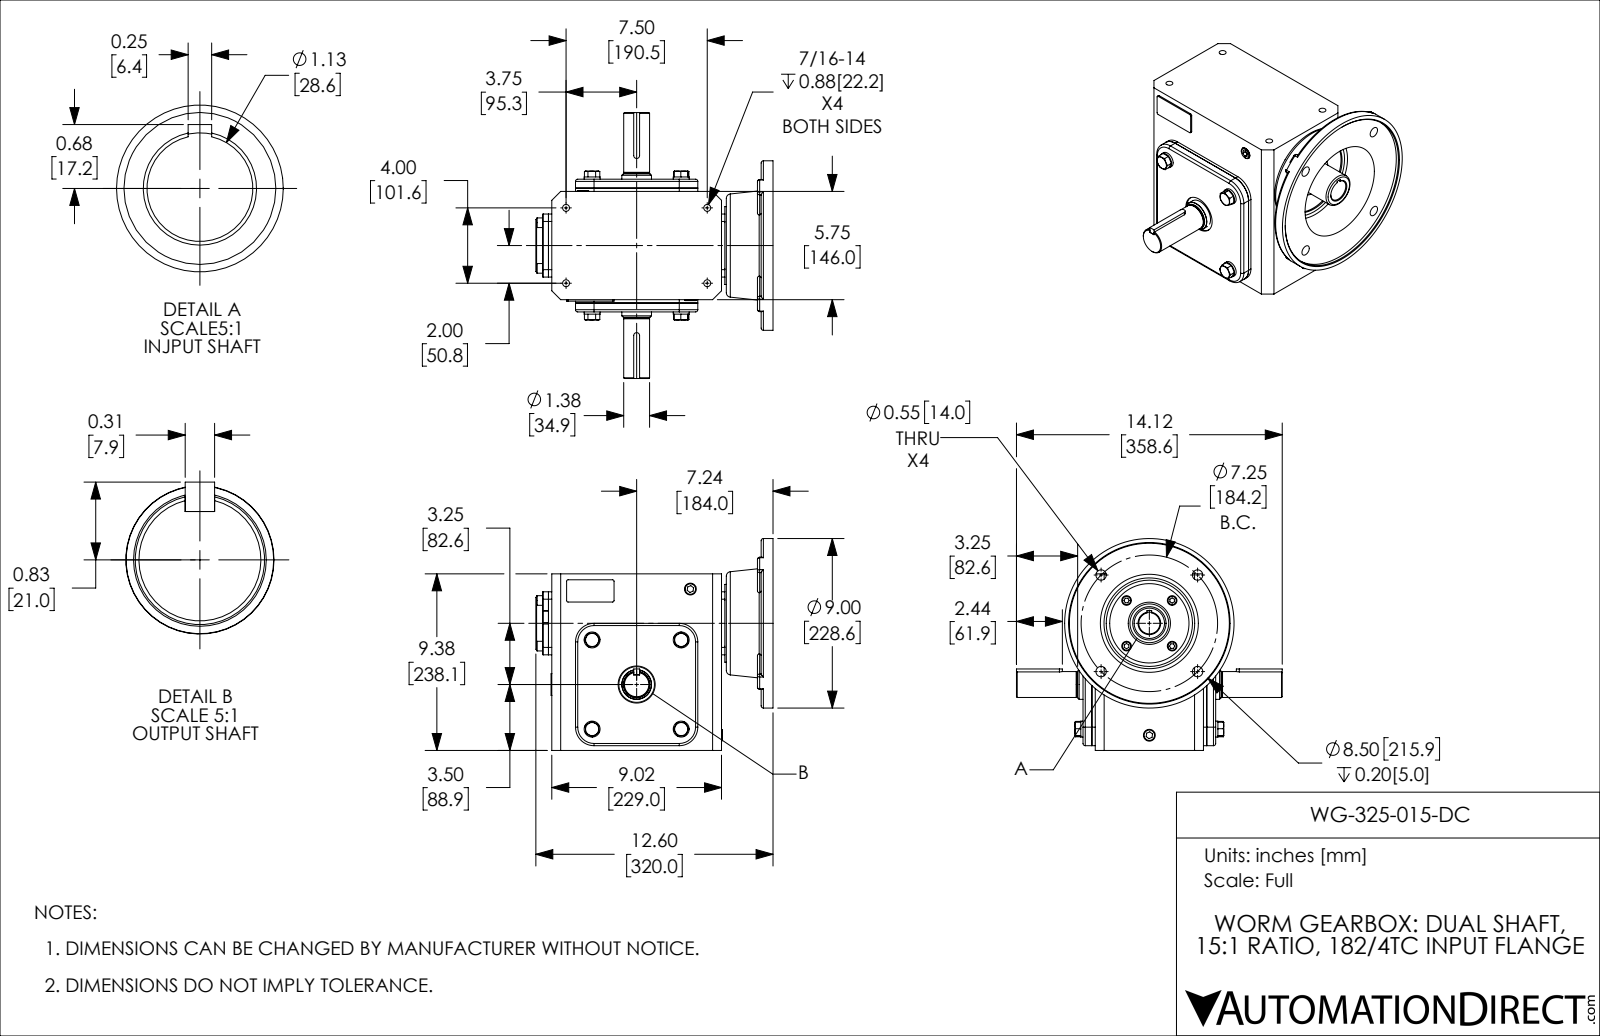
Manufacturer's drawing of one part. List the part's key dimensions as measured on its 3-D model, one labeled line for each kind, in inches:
Part name (STEP PRODUCT): WG-325-015-DC
STEP written by: SolidWorks 2017 (AUTOMOTIVE_DESIGN)
Units: inches
Bodies: 43 solids, 690 faces (349 planar, 206 cylindrical, 135 other)
Overall size (bounding box): 14.118 × 12.598 × 11.25
Volume: 542 in³ · Surface area: 1 065 in²
Round holes (diameter × count): ⌀0.354 ×4, ⌀0.368 ×4, ⌀0.551 ×4, ⌀0.628 ×3, ⌀0.591 ×1, ⌀0.978 ×1, ⌀1.125 ×1, ⌀1.181 ×1, ⌀1.969 ×1, ⌀2.244 ×1, ⌀2.441 ×1, ⌀2.756 ×1
Round bosses / shafts (diameter × count): ⌀0.846 ×4, ⌀0.512 ×4, ⌀9 ×1, ⌀4.134 ×1, ⌀2.835 ×1, ⌀1.772 ×1, ⌀1.575 ×1, ⌀1.375 ×1
Partial cylindrical surfaces — rounded edges, fillets, slot ends (radius × count): R0.118 ×18, R0.079 ×7, R0.394 ×4, R0.906 ×4, R0.984 ×4, R0.02 ×2, R0.039 ×2, R0.156 ×2
Main face-to-face distances: 0.079, 0.177, 6.496, 0.394, 6.969, 0.472, 6.575, 6.398, 0.571, 0.65
Hole centre spacings: 4.009, 1.713, 1.913, 2.422, 3.625, 5.127, 5.338, 2.372
